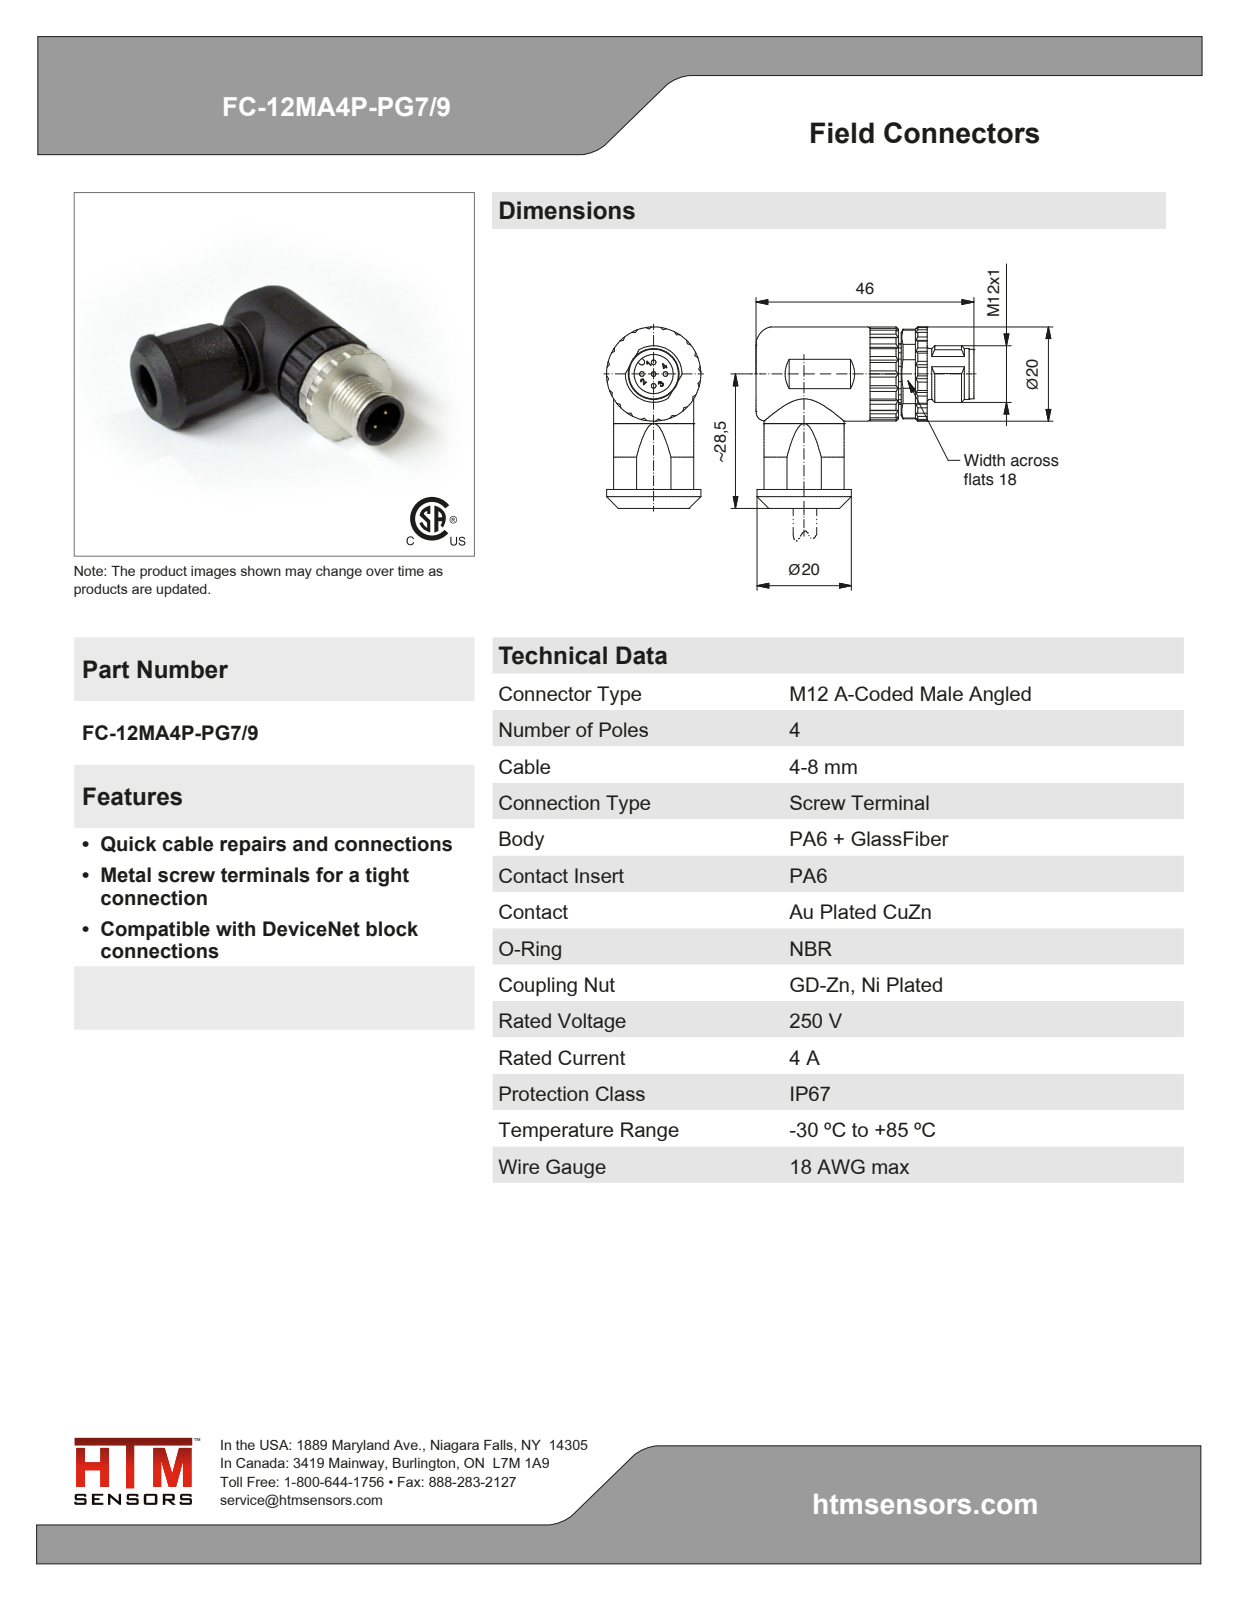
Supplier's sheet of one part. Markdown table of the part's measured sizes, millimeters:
| quantity | value |
| --- | --- |
| part name | FC-12MA4P-PG7/9 |
| STEP written by | FreeCAD (CONFIG_CONTROL_DESIGN) |
| units | millimeters |
| bodies | 1 solid, 306 faces (157 planar, 73 cylindrical, 76 other) |
| overall size | 46.2 × 38.5 × 20 |
| volume | 16 323 mm³ |
| surface area | 5 086 mm² |
| round holes (diameter × count) | 0.5 × 1, 8.3 × 1, 17.1 × 1 |
| round bosses / shafts (diameter × count) | 1 × 4, 20 × 2, 17 × 1, 13.3 × 1, 10.8 × 1, 10.5 × 1 |
| partial cylindrical surfaces (radius × count) | 0.5 × 2, 4 × 2, 0.6 × 1, 6 × 1, 9.25 × 1, 9.5 × 1 |
| main face-to-face distances | 1, 18, 17, 36.3, 30.2, 6.1, 5.45, 30.85, 0.65, 18.7 |
